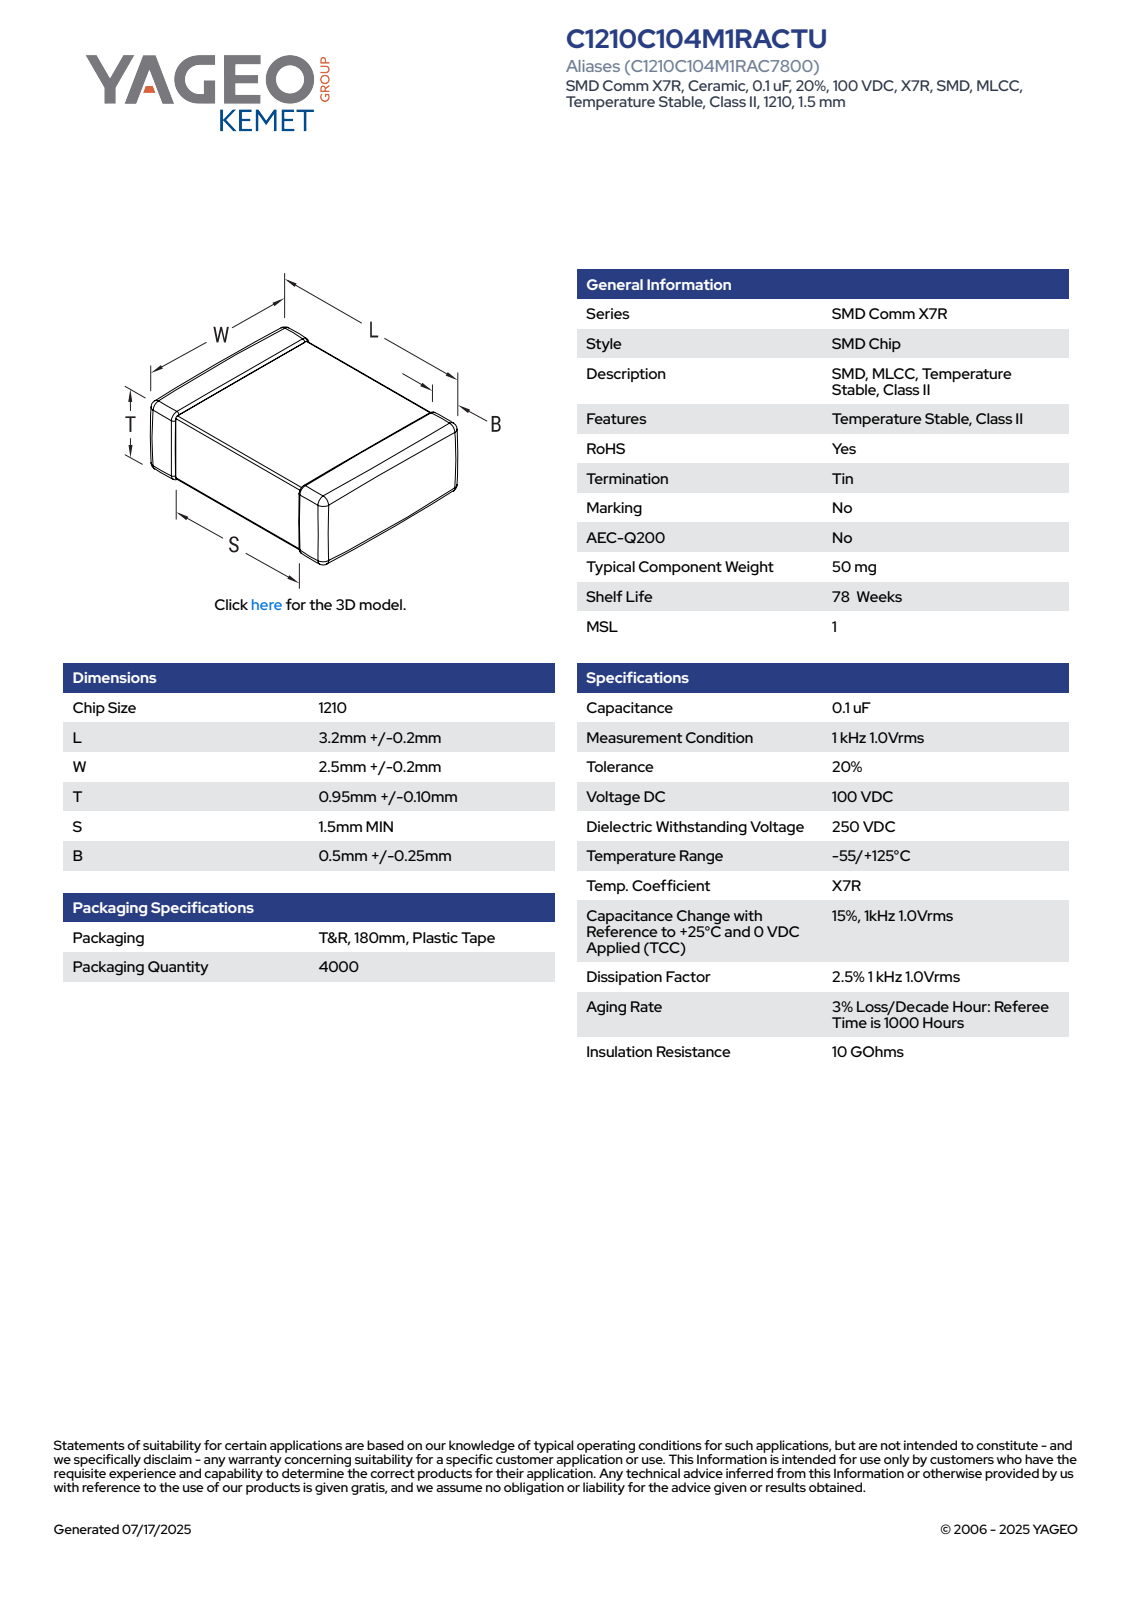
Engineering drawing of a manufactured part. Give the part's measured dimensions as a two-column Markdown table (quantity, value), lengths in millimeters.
| quantity | value |
| --- | --- |
| part name | CCS_CCSTDNOS_1210_L3.4W2.7T1.05B0.75 |
| STEP written by | SolidWorks 2014 (AUTOMOTIVE_DESIGN) |
| units | millimeters |
| bodies | 4 solids, 125 faces (71 planar, 38 cylindrical, 16 other) |
| overall size | 3.4 × 2.7 × 1.05 |
| volume | 9 mm³ |
| surface area | 30 mm² |
| main face-to-face distances | 0.99, 0.93, 1.05, 3.4, 2.64, 2.58, 2.7, 1, 0.94, 1.31 |
